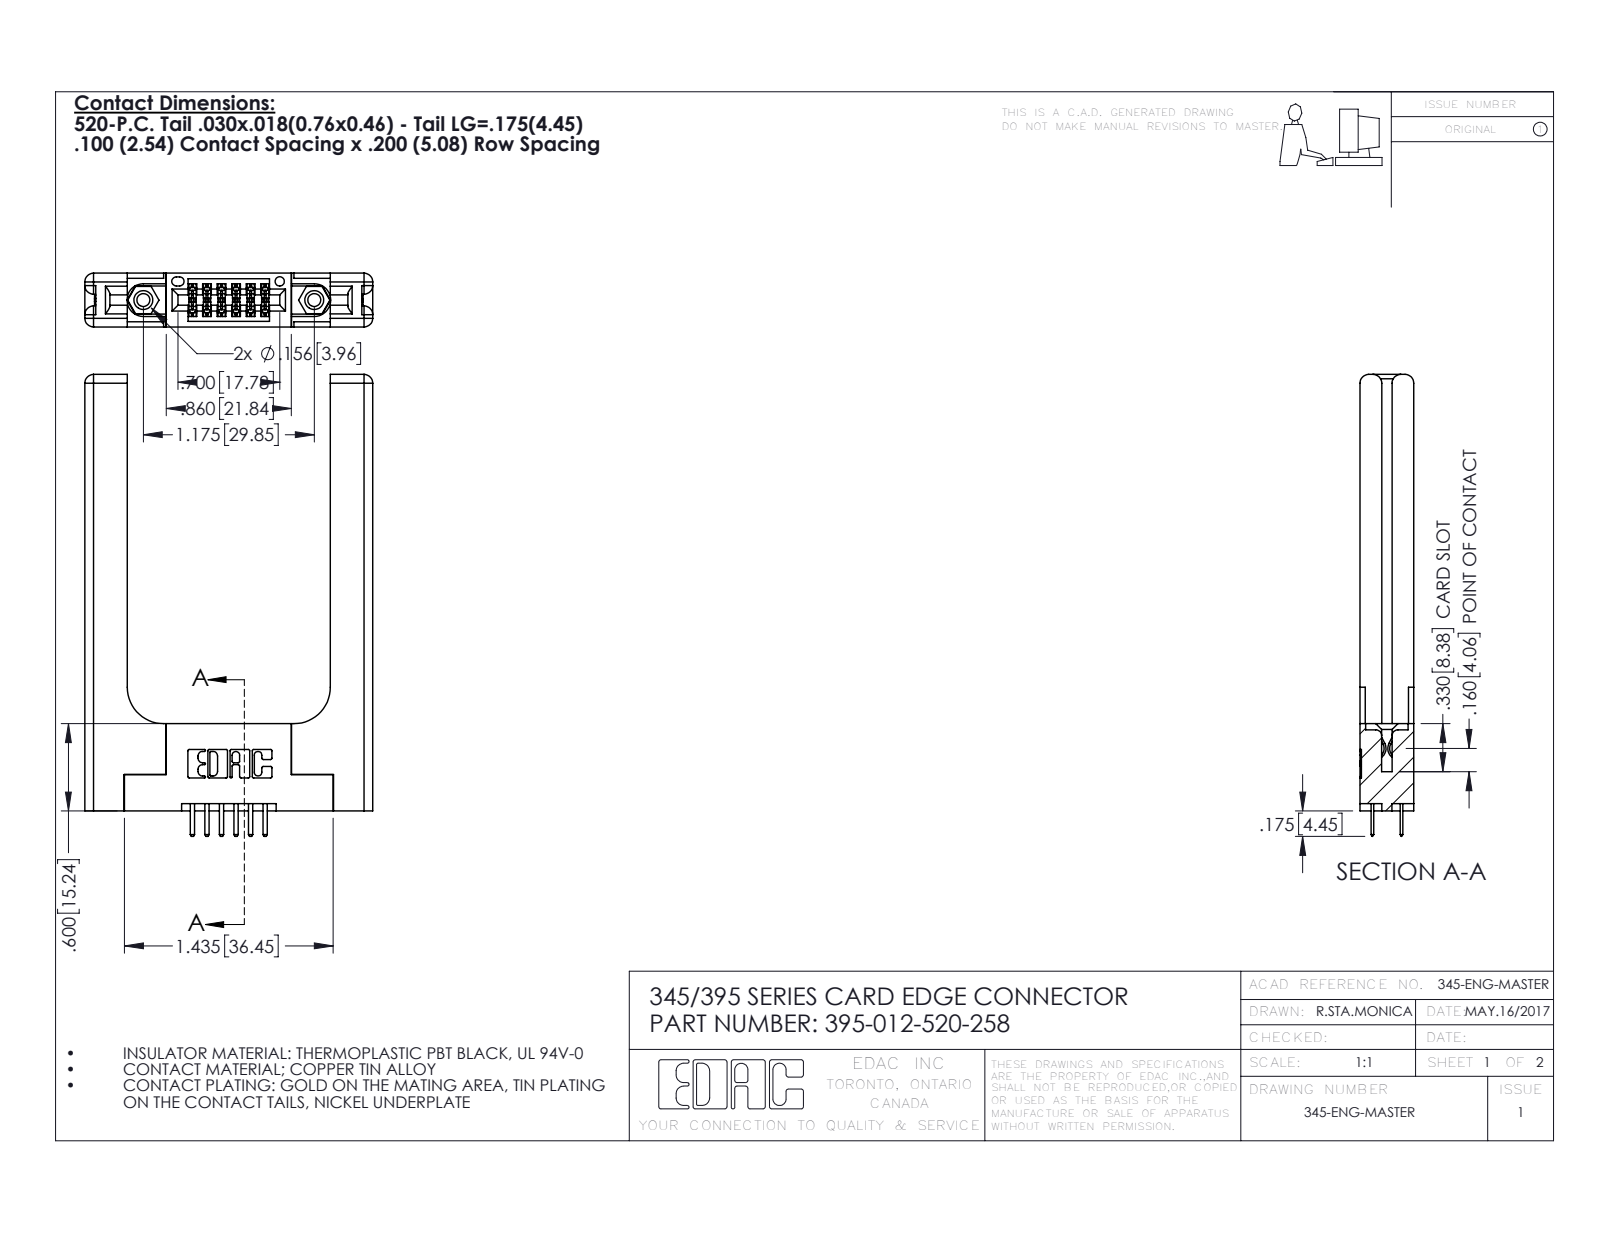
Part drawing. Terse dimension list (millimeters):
name: 345-250-001_345-250-001-102; 395-012-520-258; 345 Part_Flush Mounting Lugs - 0.156 Dia-TH; 345-220-058_345-220-058 (+1 more)
written by: SolidWorks 2016 (CONFIG_CONTROL_DESIGN)
unit: mm
bodies: 17 solids, 1030 faces (648 planar, 322 cylindrical, 60 other)
size: 80.6 × 50.3 × 9.4
volume: 13 000 mm³; area: 11 060 mm²
holes: 2× ⌀2.3, 2× ⌀3.2, 2× ⌀4, 1× ⌀1.6
bosses: 2× ⌀3.9
rounds: 22× R0.3, 18× R0.2, 16× R0.3, 16× R1.5, 6× R0.2, 6× R0.8, 3× R0.7, 2× R0.4
face distances: 9.4, 3.8, 5.6, 1.8, 35.5, 2, 7.6, 3.8, 5.1, 1.8
hole spacings: 6.9, 24, 29.8
